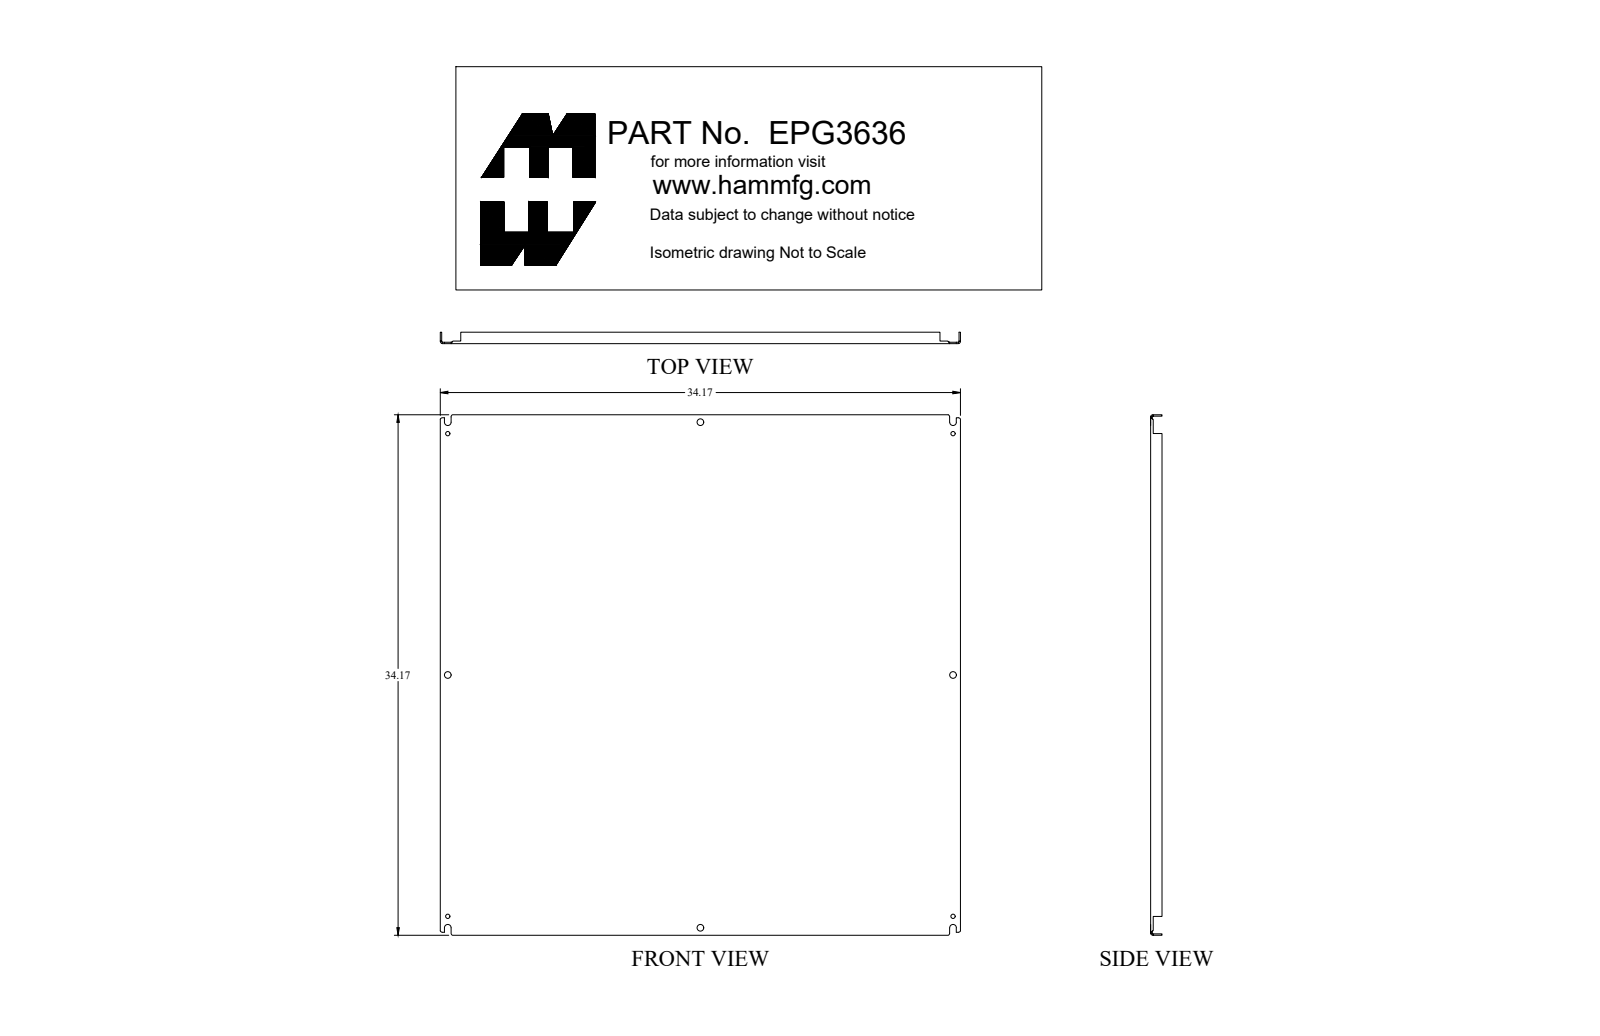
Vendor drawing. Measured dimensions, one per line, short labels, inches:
name: EPG3636
written by: SolidWorks 2018 (AUTOMOTIVE_DESIGN)
unit: in
bodies: 1 solid, 136 faces (74 planar, 46 cylindrical, 16 other)
size: 34.17 × 34.17 × 0.75
volume: 118.1 in³; area: 2 501 in²
holes: 4× ⌀0.281, 4× ⌀0.437
rounds: 4× R0.048, 4× R0.063, 4× R0.143, 4× R0.219
face distances: 0.095, 34.075, 34.17, 33.98, 0.75, 0.655, 0.171, 0.076, 0.579, 1.235
hole spacings: 15.844, 16.611, 23.468, 33.188, 36.436, 36.776, 31.688, 45.887
